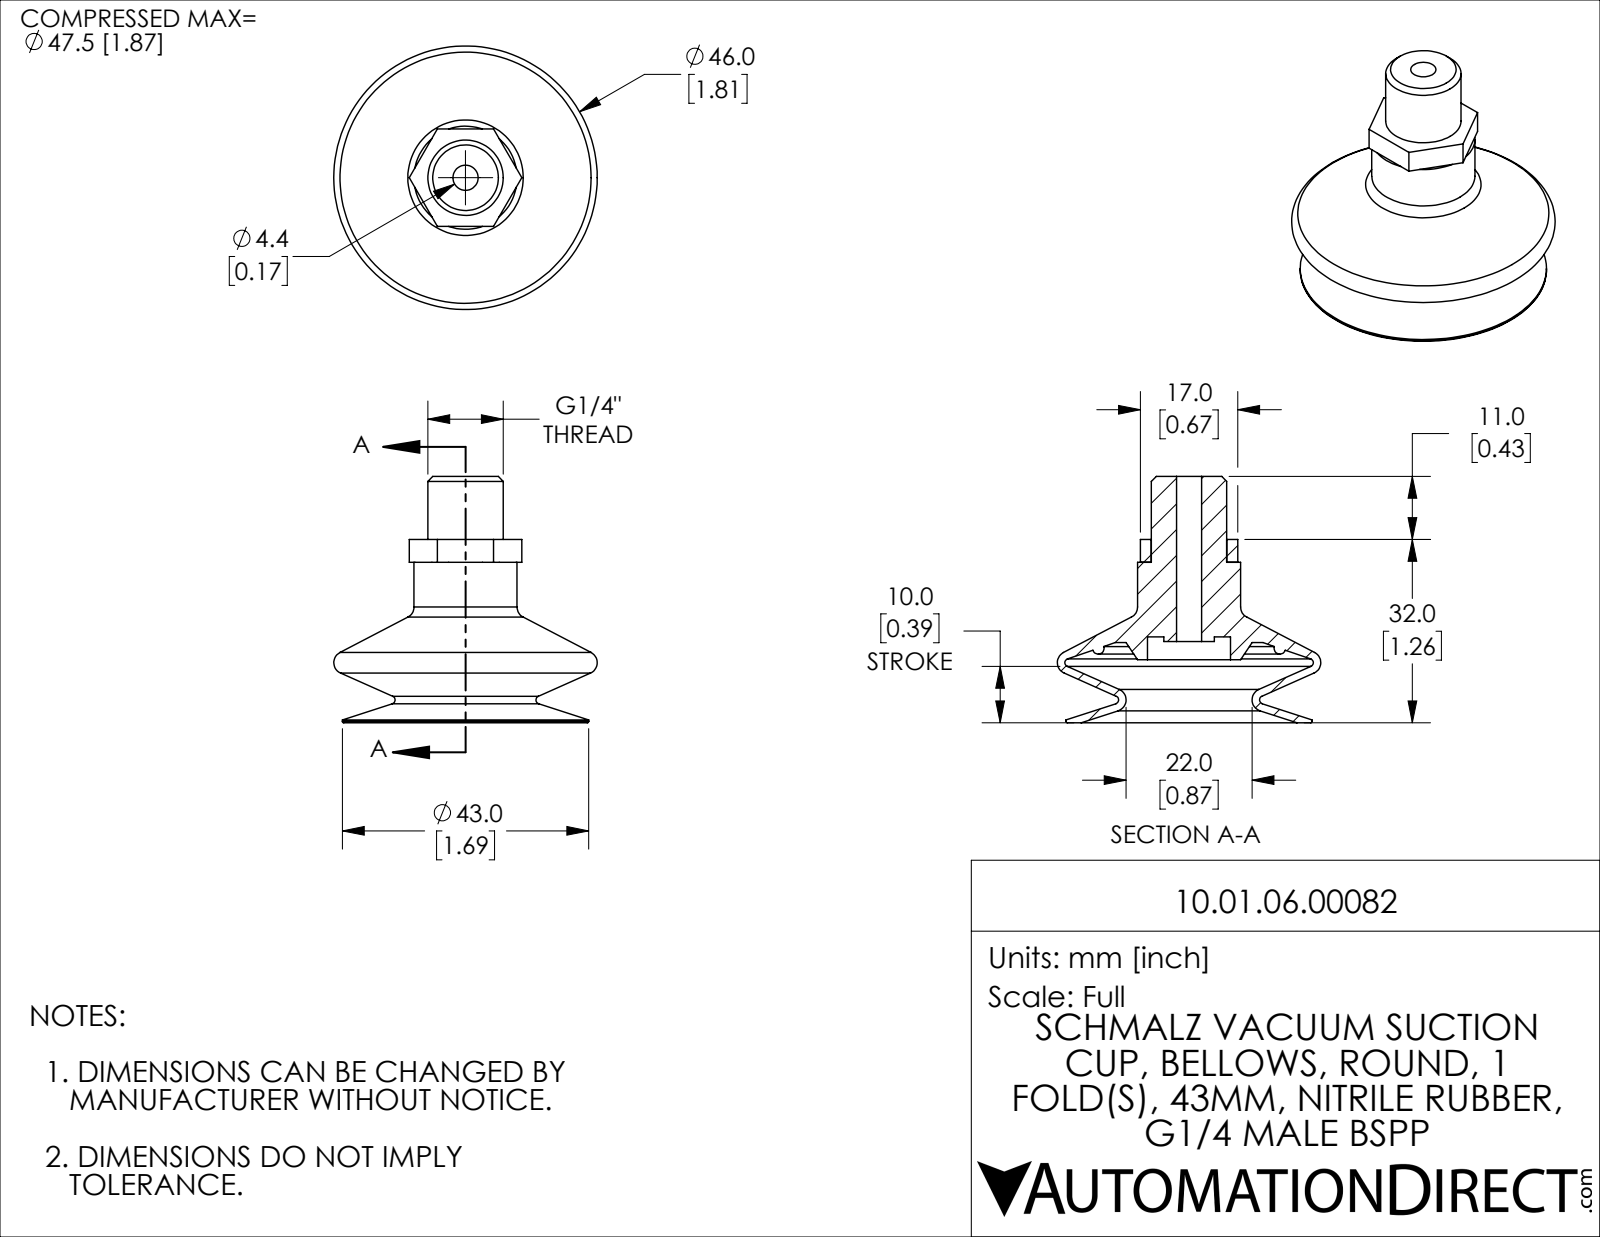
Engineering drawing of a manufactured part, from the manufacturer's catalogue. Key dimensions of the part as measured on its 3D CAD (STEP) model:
Part name (STEP PRODUCT): 10.01.06.00082
STEP written by: SolidWorks 2021 (CONFIG_CONTROL_DESIGN)
Units: millimetres
Bodies: 2 solids, 67 faces (15 planar, 14 cylindrical, 38 other)
Overall size (bounding box): 46 × 46 × 43
Volume: 12 567 mm³ · Surface area: 11 154 mm²
Round holes (diameter × count): ⌀4.4 ×1, ⌀13.16 ×1, ⌀14.5 ×1
Round bosses / shafts (diameter × count): ⌀43 ×1, ⌀18 ×1, ⌀8.8 ×1
Main face-to-face distances: 28, 17, 14, 4, 32, 15, 11, 18, 1, 13
